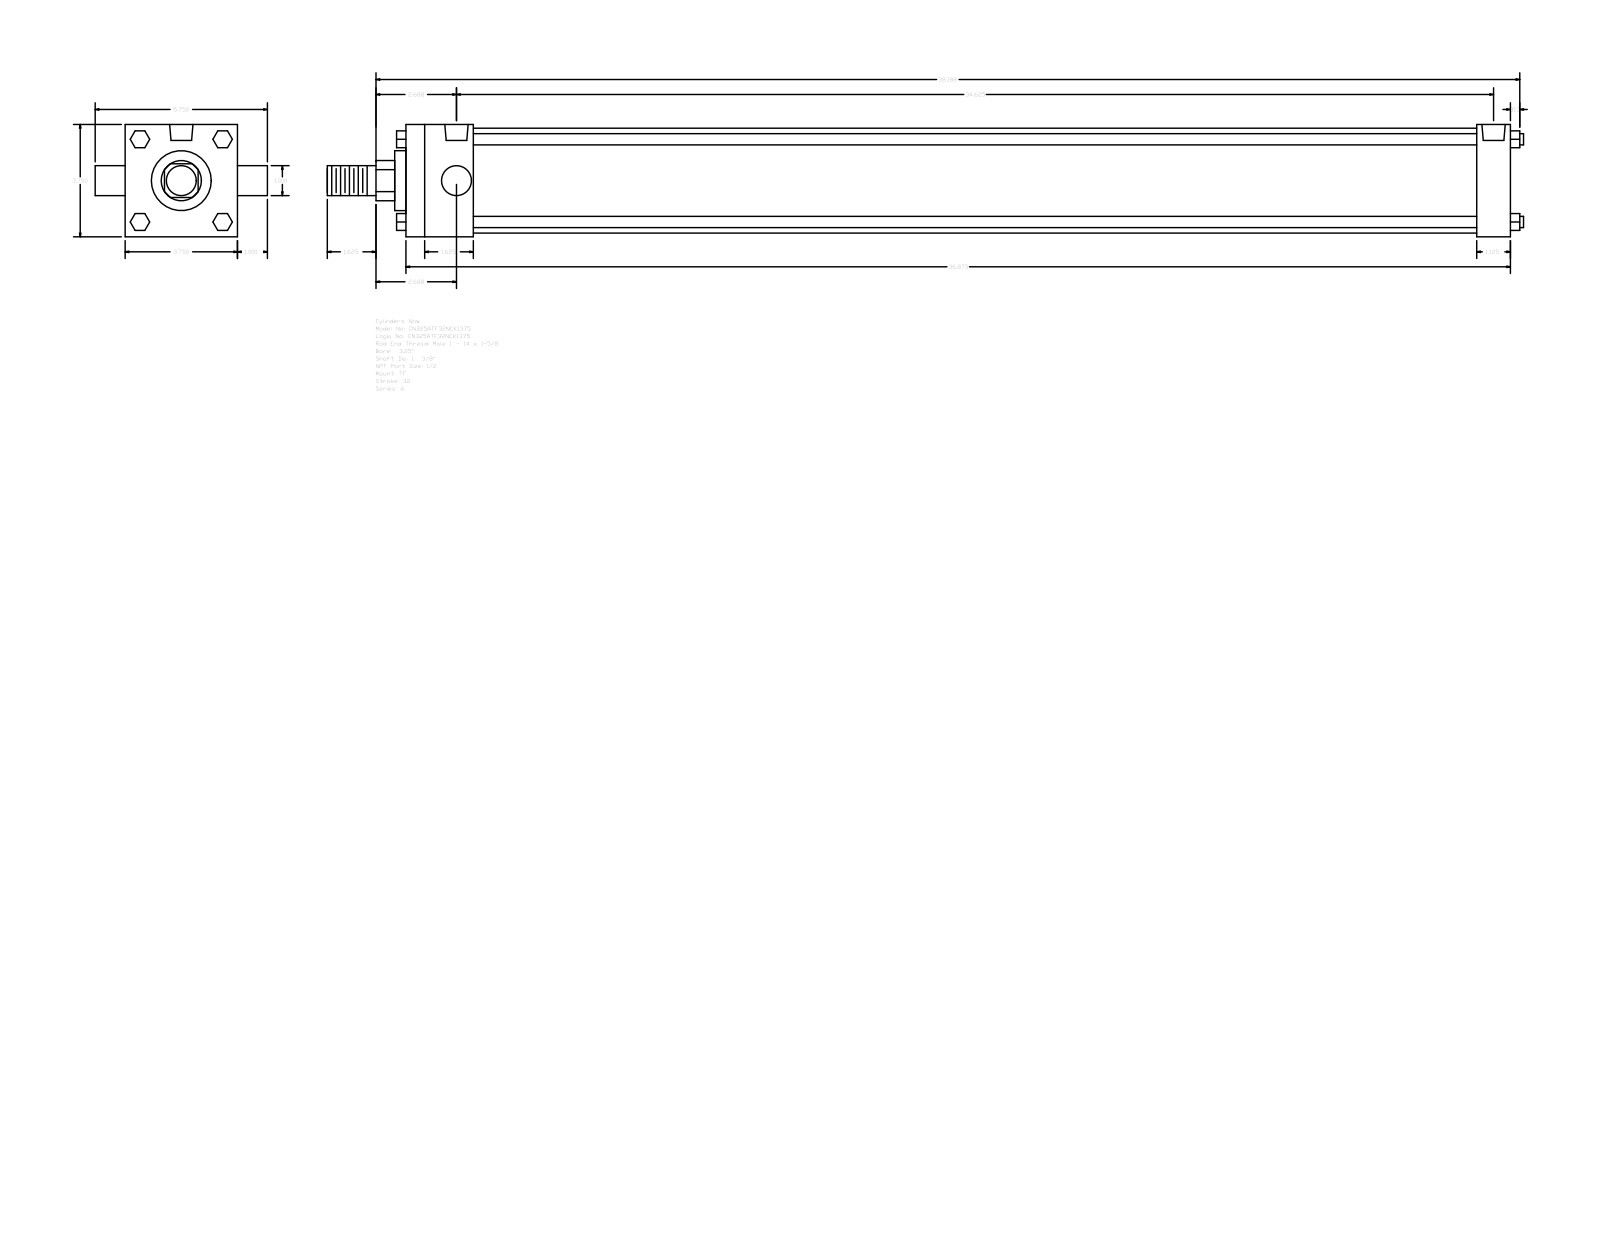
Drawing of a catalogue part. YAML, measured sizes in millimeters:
part_name: "A_TF__0325_1.375"
step_written_by: "GSSL Pune (CONFIG_CONTROL_DESIGN)"
units: millimeters
bodies: {solids: 0, faces: 120, planar: 92, cylindrical: 28, other: 0}
overall_size: [1014.41, 146.05, 95.25]
round_holes:
  - {diameter: 8.73, count: 3}
  - {diameter: 19.77, count: 2}
round_bosses_or_shafts:
  - {diameter: 9.53, count: 4}
  - {diameter: 25.4, count: 2}
  - {diameter: 88.9, count: 1}
  - {diameter: 50.8, count: 1}
  - {diameter: 34.92, count: 1}
partial_cylinders:
  - {radius: 17.06, count: 1}
face_to_face_distances: [95.24, 936.62, 57.15, 908.05, 850.9, 879.47, 28.57, 66.67, 9.52, 917.57]
hole_center_spacings: [3.18, 876.3, 873.12, 879.48]
